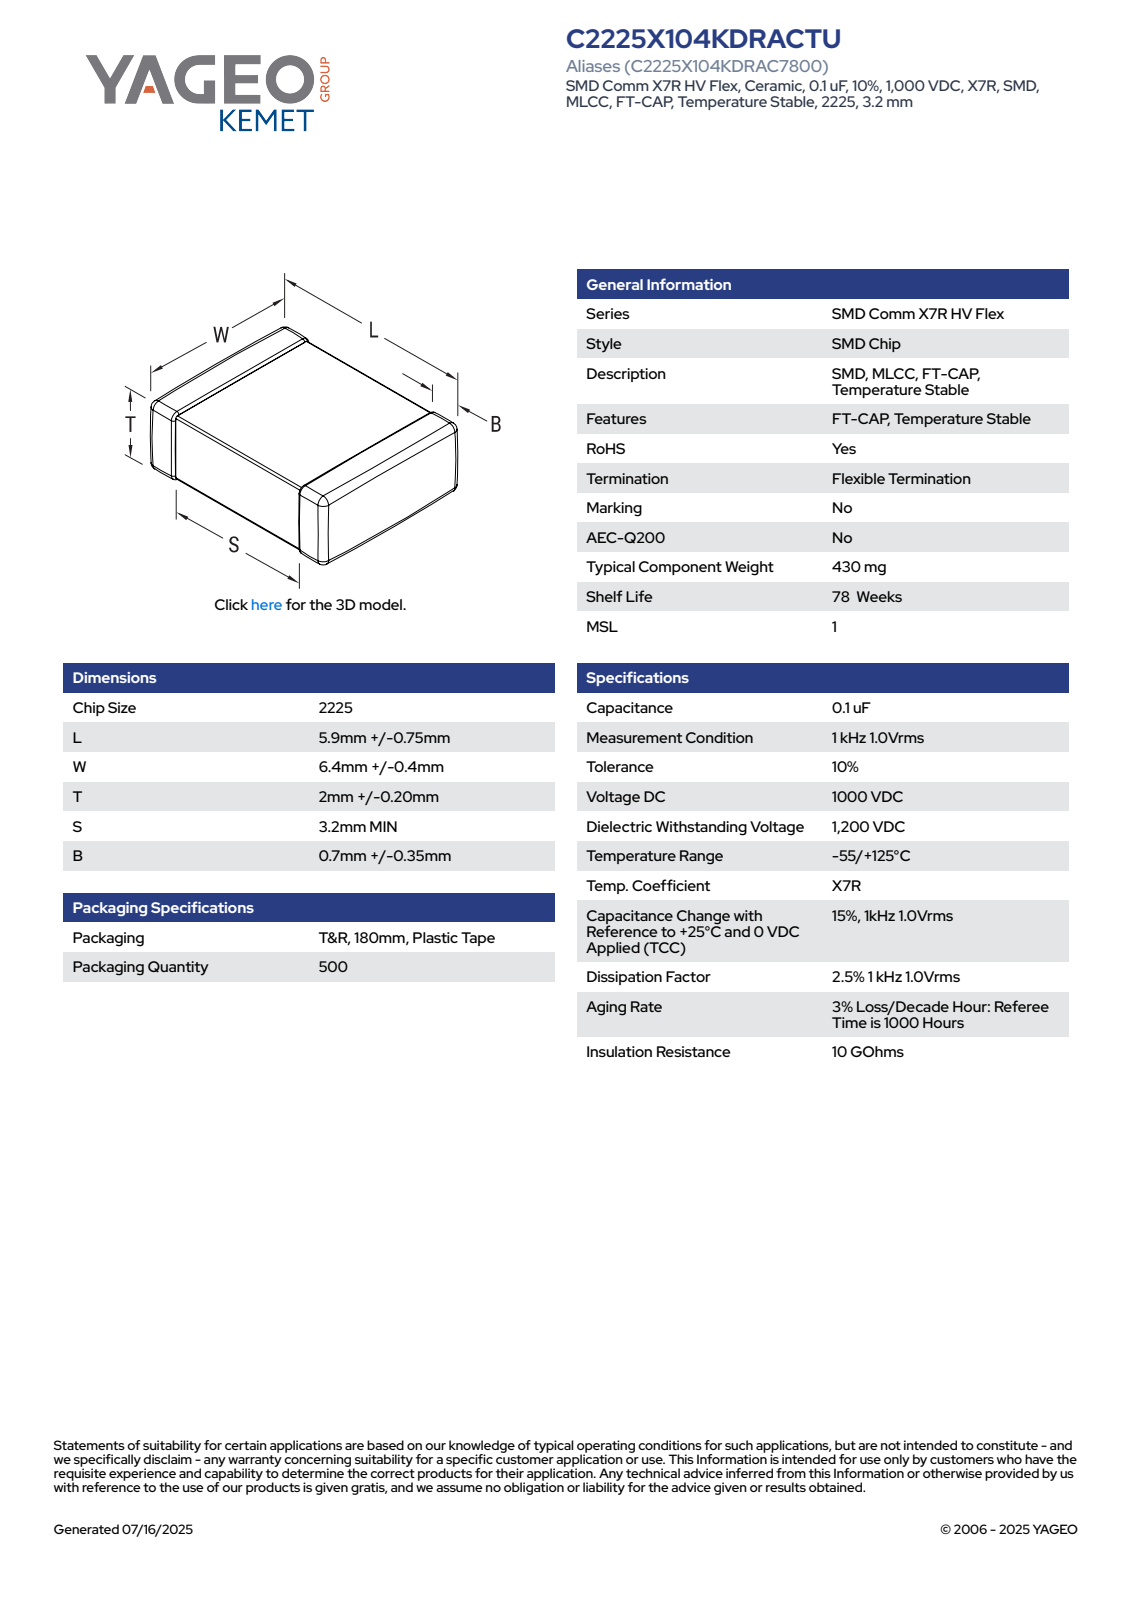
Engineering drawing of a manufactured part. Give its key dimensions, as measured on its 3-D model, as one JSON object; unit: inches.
{"part_name": "CCS_CCSTD_2225_L6.65W6.8T2.2B0.7", "step_written_by": "SolidWorks 2021 (AUTOMOTIVE_DESIGN)", "units": "inches", "bodies": {"solids": 4, "faces": 125, "planar": 71, "cylindrical": 38, "other": 16}, "overall_size": [0.268, 0.262, 0.087], "volume_in3": 0.005, "surface_area_in2": 0.231, "partial_cylinders_radius": [[0.006, 24]], "face_to_face_distances": [0.076, 0.081, 0.262, 0.087, 0.257, 0.262, 0.268, 0.039, 0.102, 0.16]}
